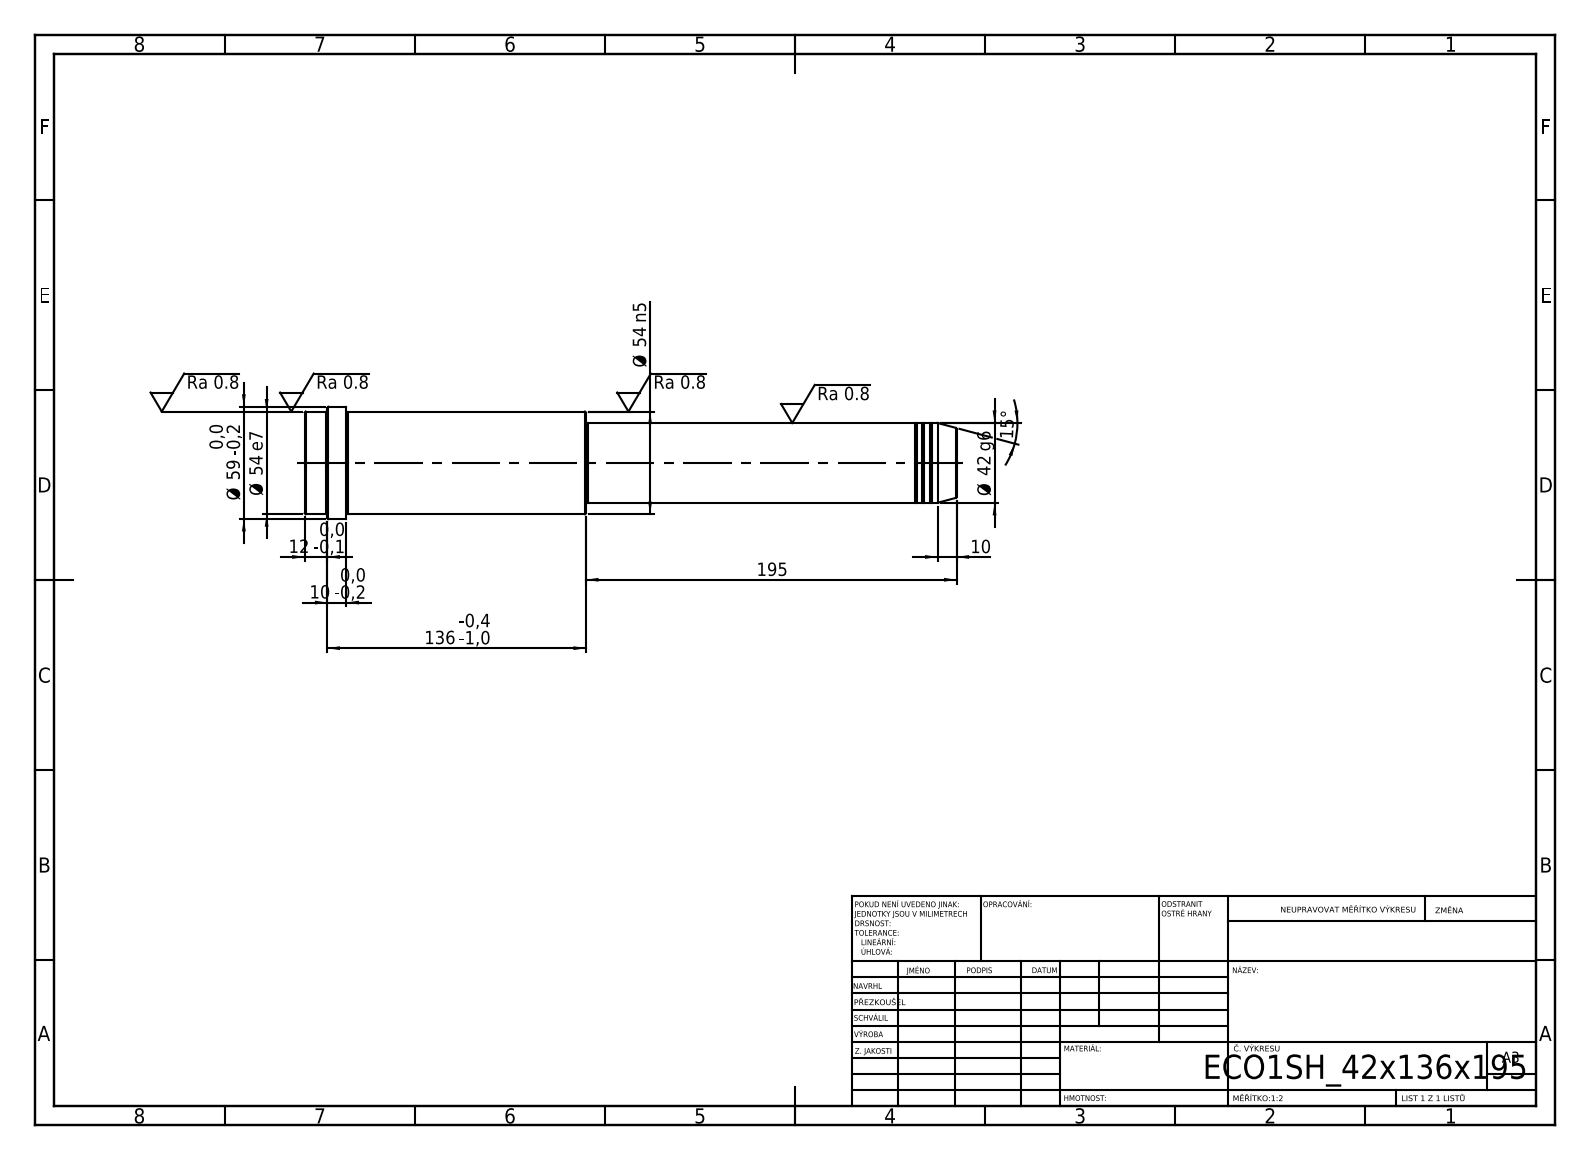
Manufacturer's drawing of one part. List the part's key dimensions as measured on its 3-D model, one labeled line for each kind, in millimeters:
STEP written by: SolidWorks 2019 (CONFIG_CONTROL_DESIGN)
Units: millimetres
Bodies: 1 solid, 52 faces (6 planar, 16 cylindrical, 30 other)
Overall size (bounding box): 343 × 59 × 59
Volume: 611 439 mm³ · Surface area: 56 454 mm²
Round bosses / shafts (diameter × count): ⌀59 ×1, ⌀54 ×1, ⌀42 ×1, ⌀41 ×1
Main face-to-face distances: 343, 195, 148, 321, 126, 22, 331, 136, 10, 12
